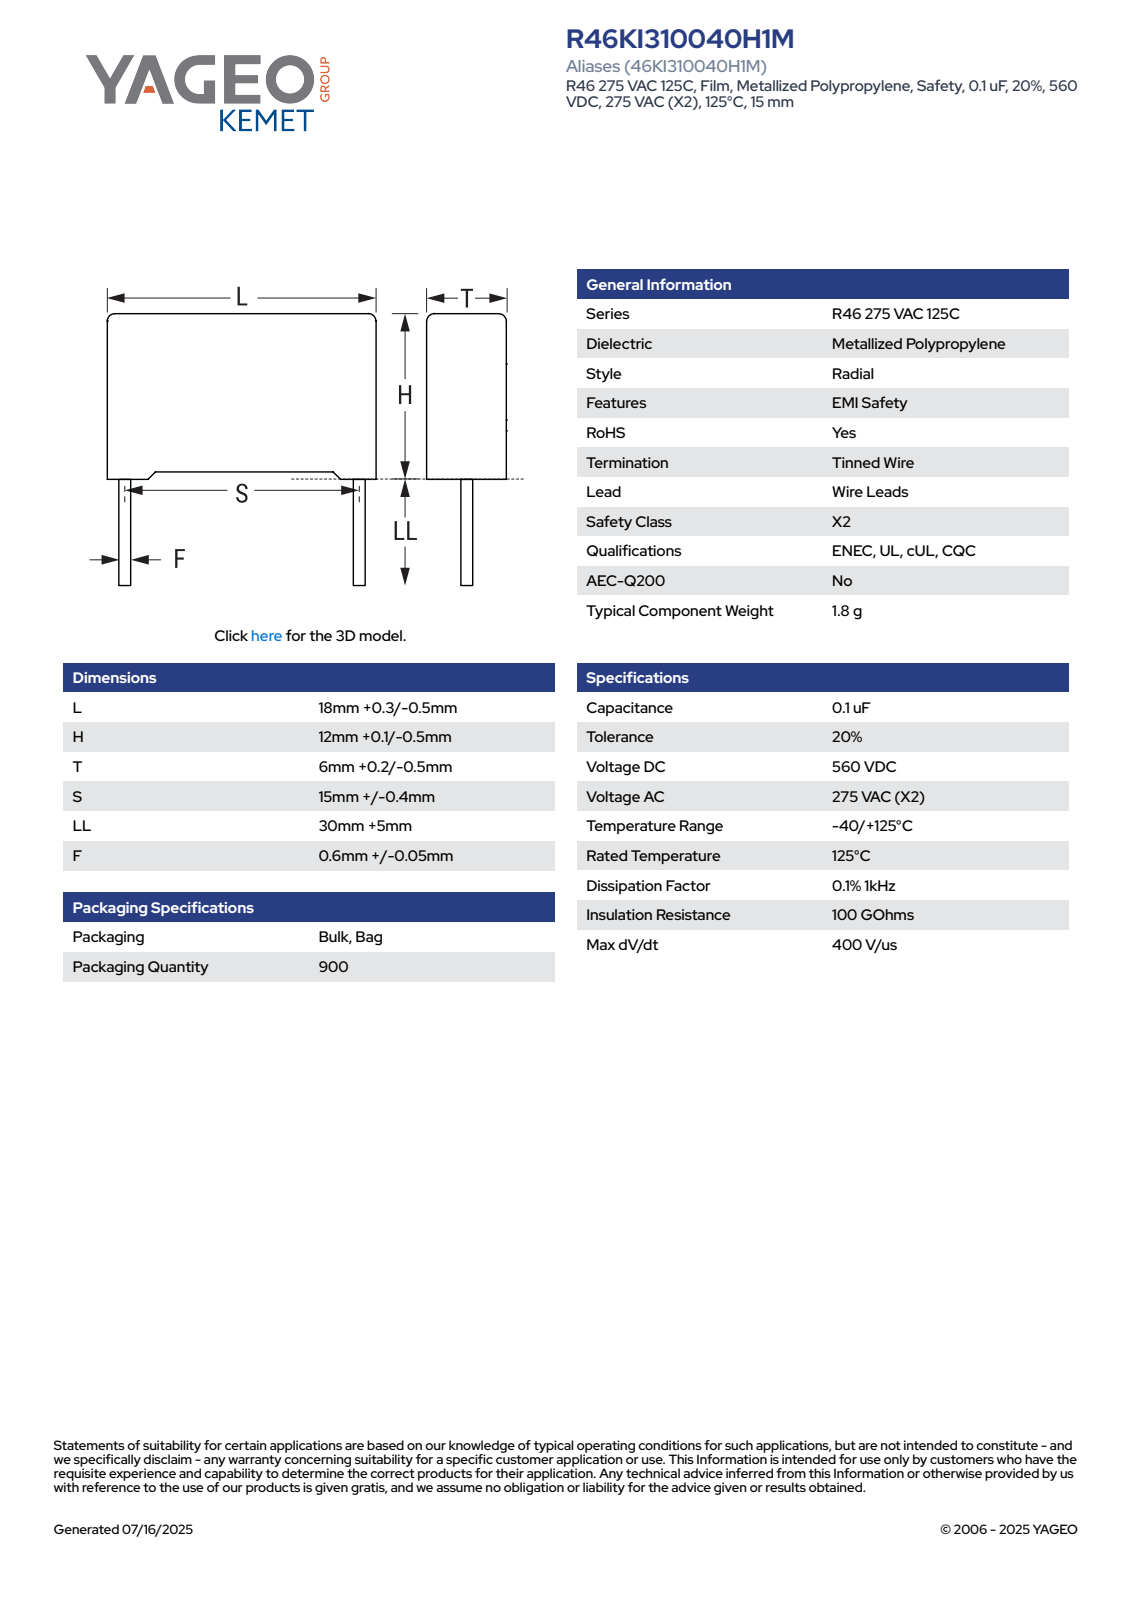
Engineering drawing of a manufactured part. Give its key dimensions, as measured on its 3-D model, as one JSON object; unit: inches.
{"part_name": "CFR_RB2_18X12X6_L18.3H12.1T6.2S15LL35F0.65", "step_written_by": "SolidWorks 2021 (AUTOMOTIVE_DESIGN)", "units": "inches", "bodies": {"solids": 4, "faces": 85, "planar": 77, "cylindrical": 8, "other": 0}, "overall_size": [1.854, 0.72, 0.244], "volume_in3": 0.081, "surface_area_in2": 1.54, "round_bosses_or_shafts": [[0.026, 2]], "partial_cylinders_radius": [[0.02, 4]], "face_to_face_distances": [0.244, 0.447, 0.72, 0.024, 0.22, 0.03, 0.476, 0.017, 0.013, 0.46]}
